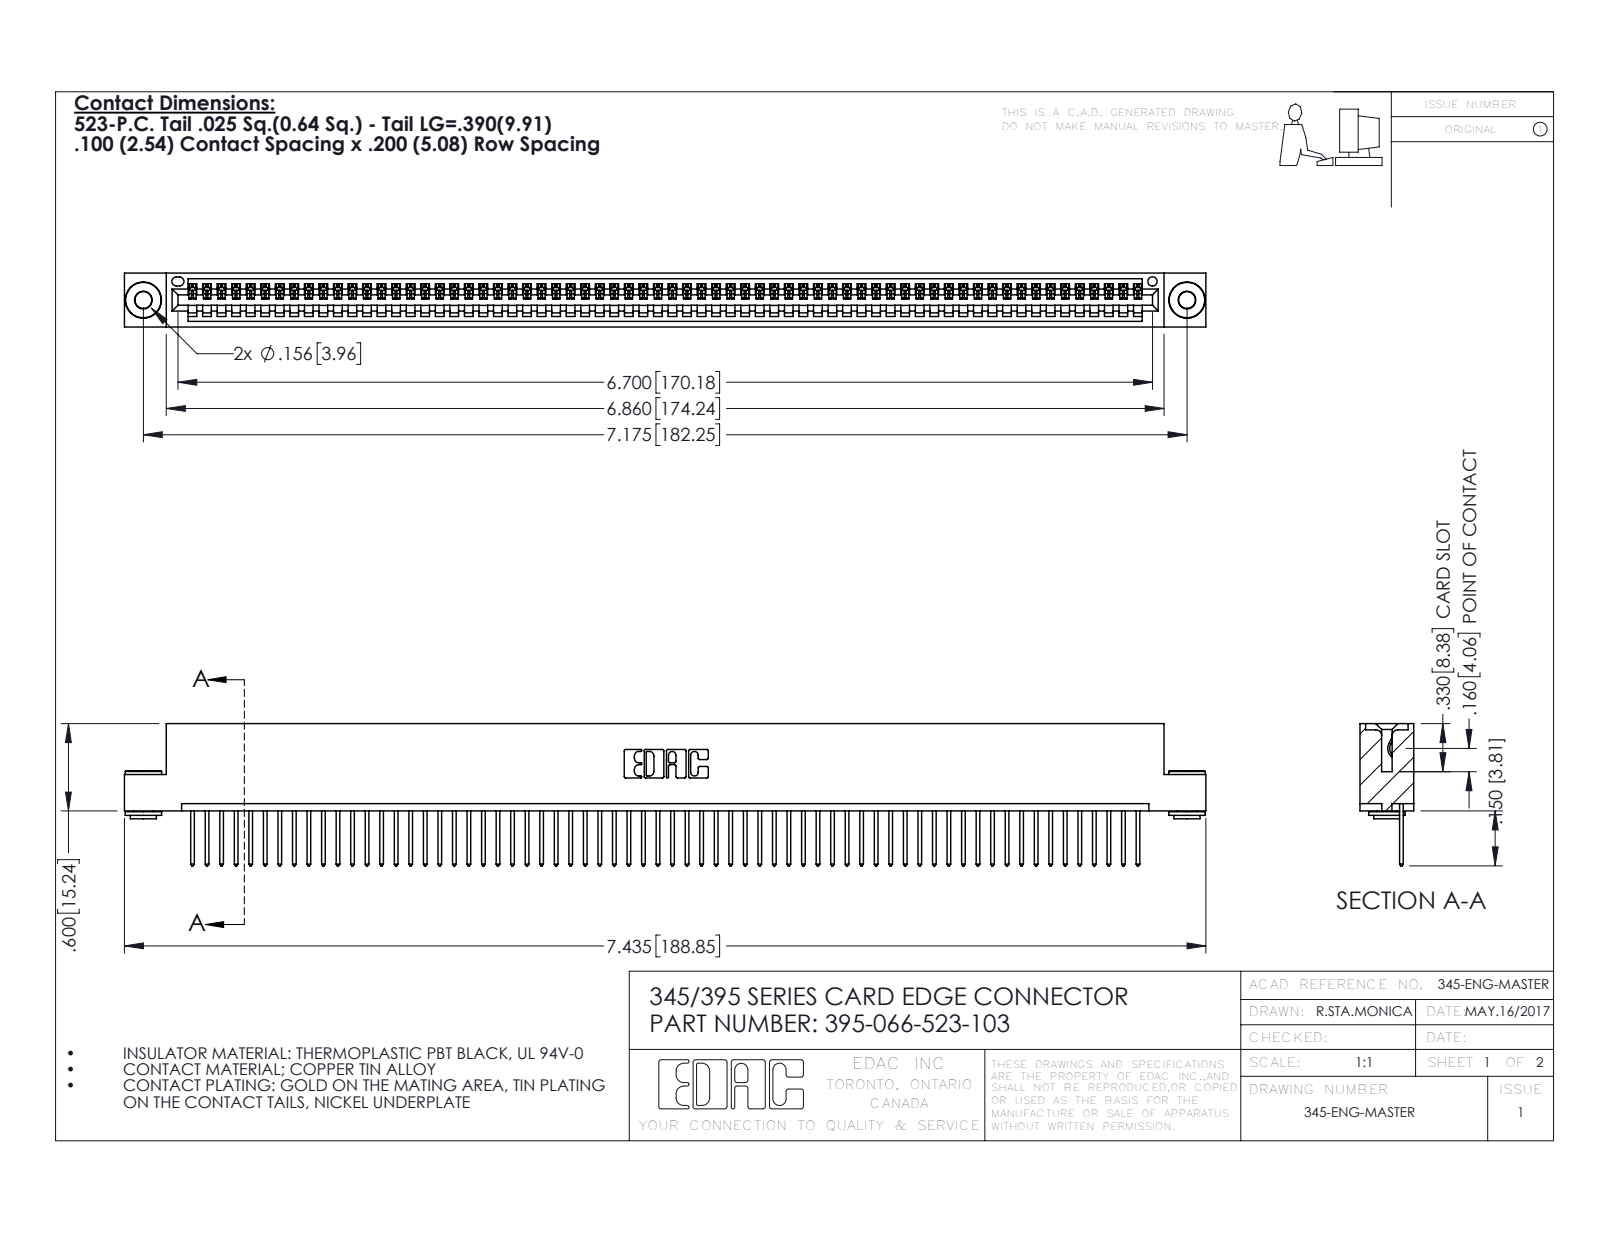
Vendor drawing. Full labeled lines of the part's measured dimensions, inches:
Part name (STEP PRODUCT): 345 Part_Flush Mounting Lugs - 0.156 Dia-TH; 345-250-002_345-250-002-102; 345-292-001_345-293-123; 395-066-523-103
STEP written by: SolidWorks 2016 (CONFIG_CONTROL_DESIGN)
Units: inches
Bodies: 69 solids, 3992 faces (2730 planar, 1254 cylindrical, 8 other)
Overall size (bounding box): 7.435 × 0.977 × 0.37
Volume: 1.106 in³ · Surface area: 38.29 in²
Round holes (diameter × count): ⌀0.116 ×2, ⌀0.156 ×2, ⌀0.064 ×1
Round bosses / shafts (diameter × count): ⌀0.25 ×2, ⌀0.18 ×2, ⌀0.136 ×2
Partial cylindrical surfaces — rounded edges, fillets, slot ends (radius × count): R0.006 ×132, R0.01 ×132, R0.01 ×22, R0.007 ×6, R0.031 ×6, R0.026 ×3, R0.031 ×2, R0.04 ×2
Main face-to-face distances: 0.072, 0.298, 0.37, 0.2, 0.025, 0.098, 0.272, 0.225, 0.149, 0.072
Hole centre spacings: 0.27, 6.939, 7.175
